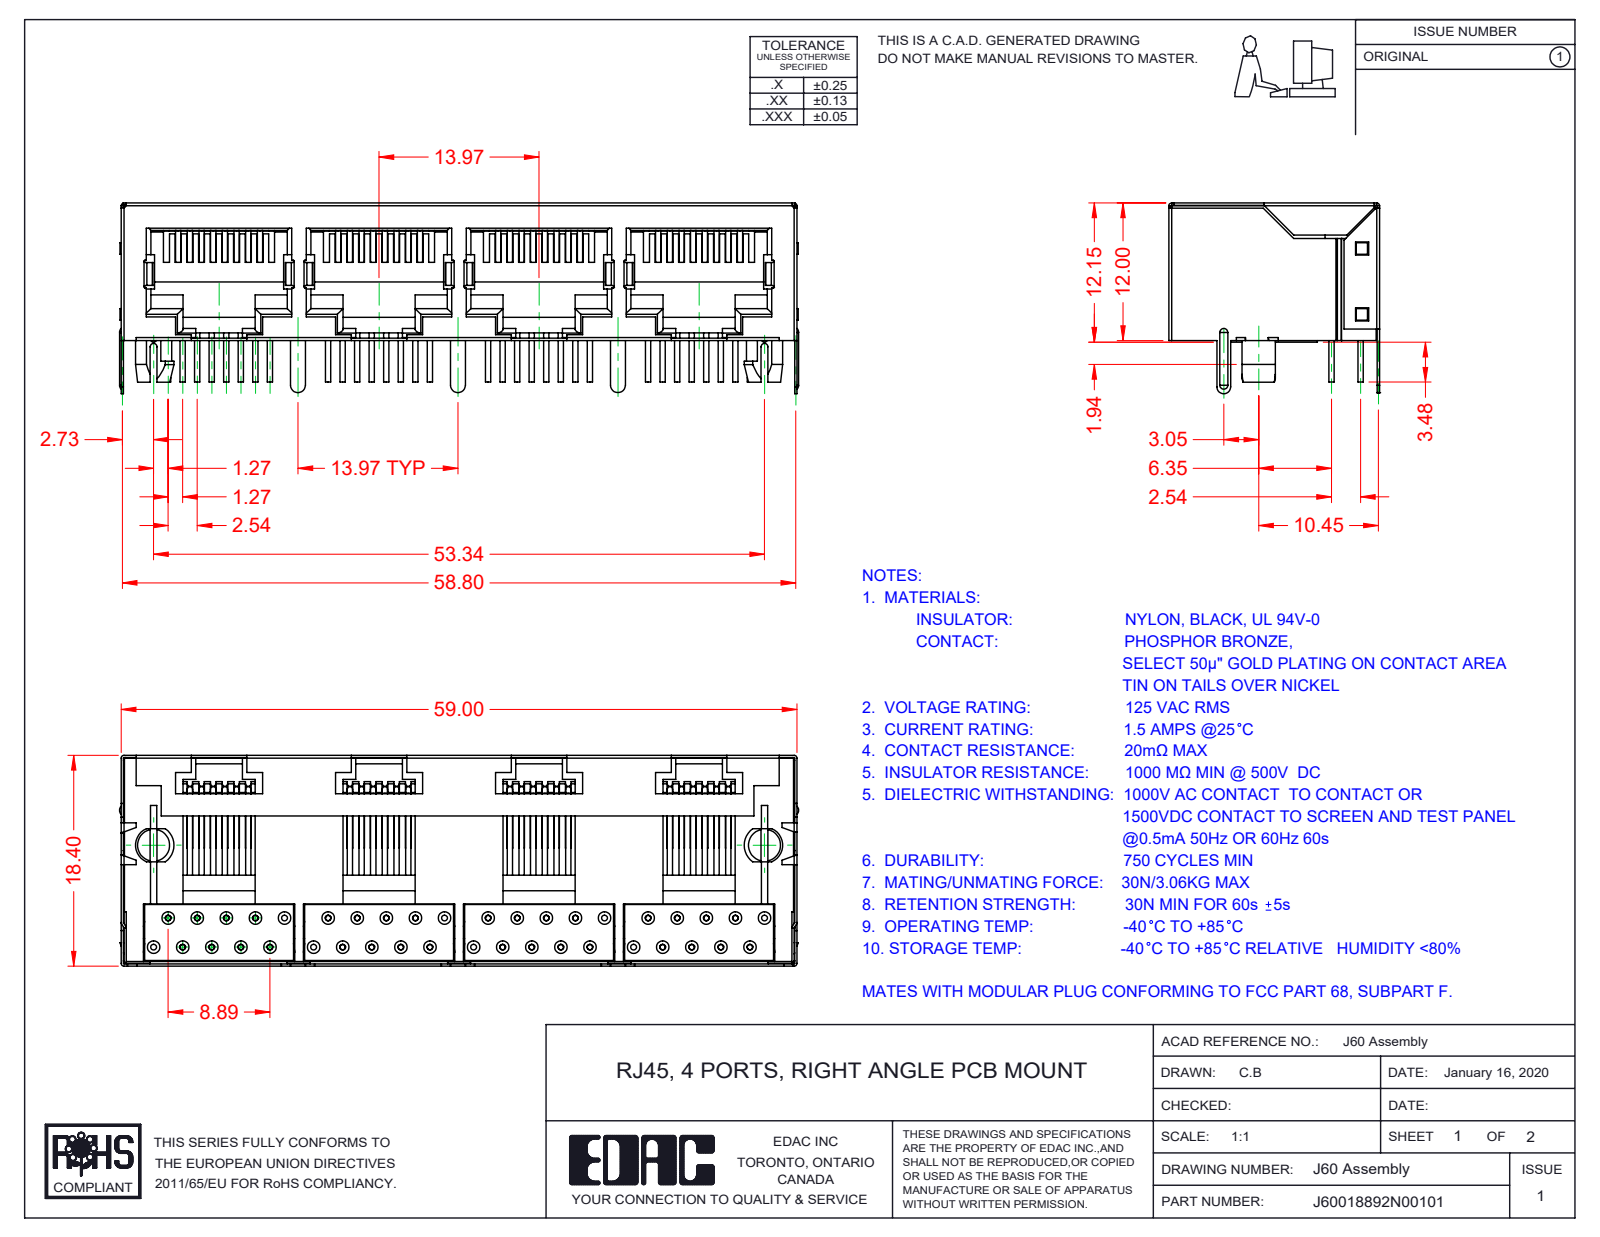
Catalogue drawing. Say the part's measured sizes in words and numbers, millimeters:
The part is named "60 Shield; RJ60048892N00101; 60 Insulator; 60 Contacts_8P8C". Its 3-D file was written by "SolidWorks 2016 (CONFIG_CONTROL_DESIGN)". It is 34 solids with 2562 faces: 1489 planar, 715 cylindrical and 358 other. Overall it measures 59.3 by 18.4 by 16.65 millimeters. Its volume is 7 013 cubic millimeters and its surface area 18 560 square millimeters. Round holes: 40 of diameter 0.5, 40 of diameter 1.1. Round bosses or shafts: 96 of diameter 0.46. Partial cylindrical surfaces (rounded edges, fillets, slot ends): 26 of radius 0.3, 21 of radius 0.25, 18 of radius 0.5, 16 of radius 0.1, 10 of radius 0.21, 7 of radius 0.8, 3 of radius 0.65, 2 of radius 0.28. The main face-to-face distances are 0.5, 11.75, 11.55, 13.97, 2.19, 5.38, 5.18, 4.88, 18.2, 11.5. The hole center spacings are 2.84, 2.54, 4.58, 13.97, 5.08, 12.95, 15.45, 11.43.
